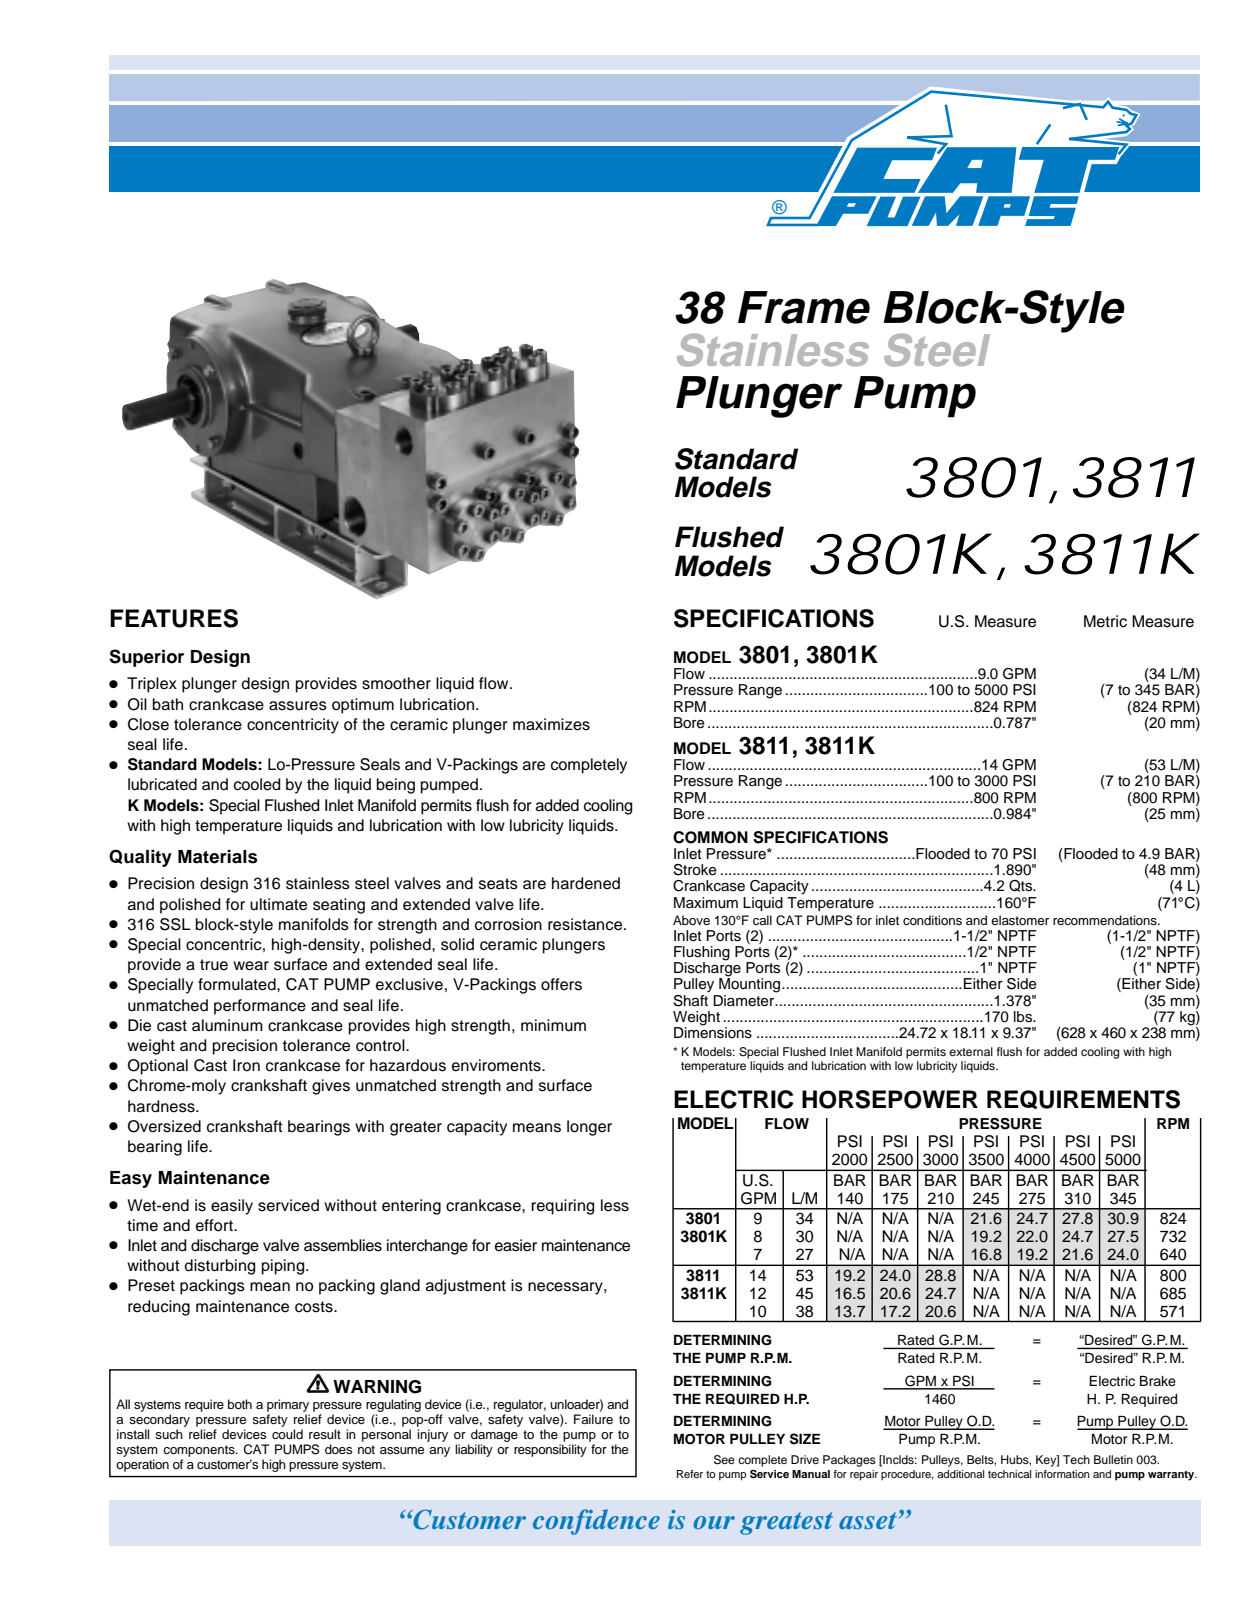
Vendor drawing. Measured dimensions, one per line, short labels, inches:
name: 3801
written by: SolidWorks 2020 (CONFIG_CONTROL_DESIGN)
unit: in
bodies: 0 solids, 2504 faces (980 planar, 534 cylindrical, 990 other)
size: 24.803 × 18.11 × 9.744
holes: 8× ⌀0.433, 4× ⌀0.33, 4× ⌀0.466, 3× ⌀0.451, 1× ⌀0.266, 1× ⌀0.34, 1× ⌀0.591, 1× ⌀1.141, 1× ⌀1.417, 1× ⌀1.732, 1× ⌀1.937, 1× ⌀1.969
bosses: 36× ⌀0.63, 12× ⌀0.709, 8× ⌀0.61, 8× ⌀0.606, 4× ⌀0.827, 4× ⌀0.724, 2× ⌀1.772, 2× ⌀0.48
rounds: 44× R0.079, 37× R0.394, 22× R0.118, 14× R0.059, 11× R0.157, 10× R0.197, 10× R0.63, 7× R0.039
face distances: 0.315, 3.543, 3.346, 6.89, 0.719, 9.774, 0.669, 9.055, 0.404, 9.459
hole spacings: 2.717, 3.045, 4.226, 4.643, 5.981, 6.562, 8.341, 2.441
